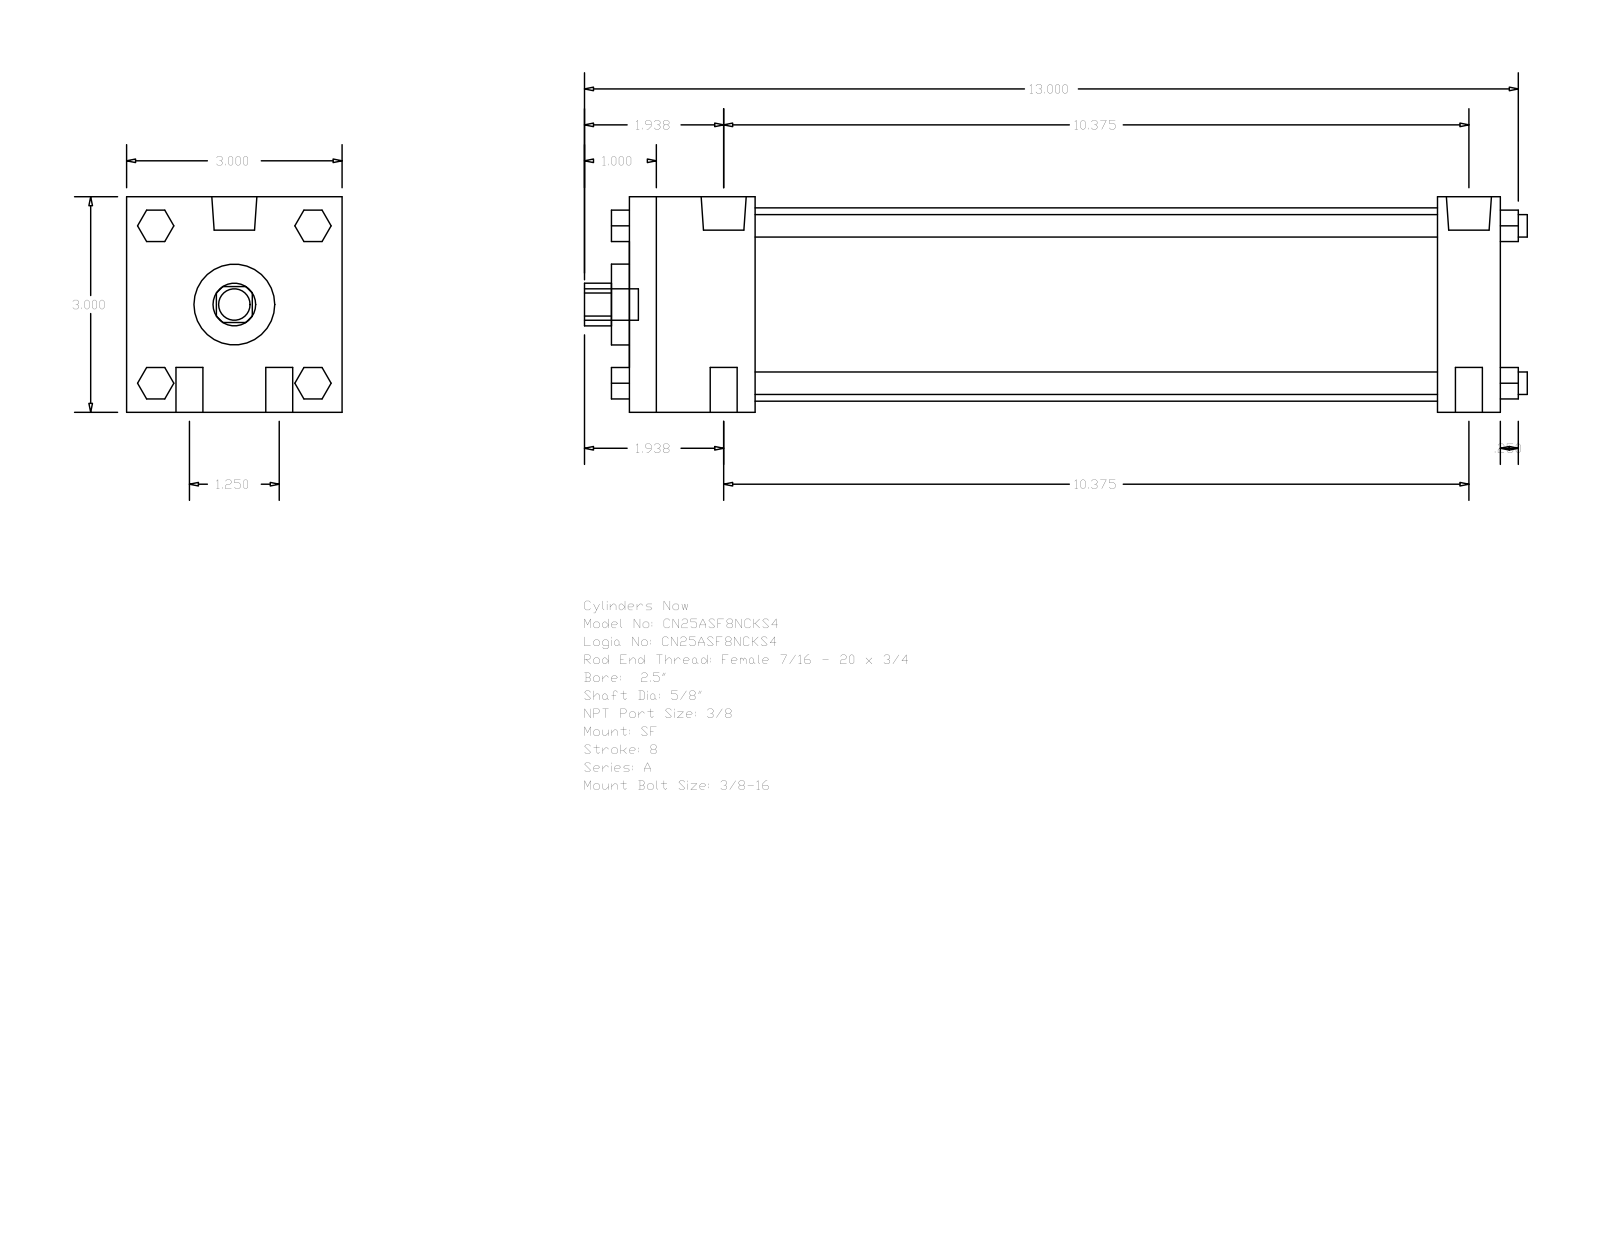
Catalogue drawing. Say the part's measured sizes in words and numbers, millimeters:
The part is named "A_SF__0250_0.625". Its 3-D file was written by "GSSL Pune (CONFIG_CONTROL_DESIGN)". It is 0 solids with 124 faces: 94 planar, 30 cylindrical and 0 other. Overall it measures 333.38 by 76.2 by 76.2 millimeters. Round holes: 1 of diameter 15.88, 1 of diameter 28.57, 1 of diameter 68.33. Round bosses or shafts: 4 of diameter 9.53, 4 of diameter 7.94, 2 of diameter 15.93, 2 of diameter 5.56, 1 of diameter 11.11. Partial cylindrical surfaces (rounded edges, fillets, slot ends): 1 of radius 7.54. The main face-to-face distances are 76.2, 307.97, 44.45, 285.74, 22.23, 241.29, 263.52, 6.35, 314.32, 50.8.
